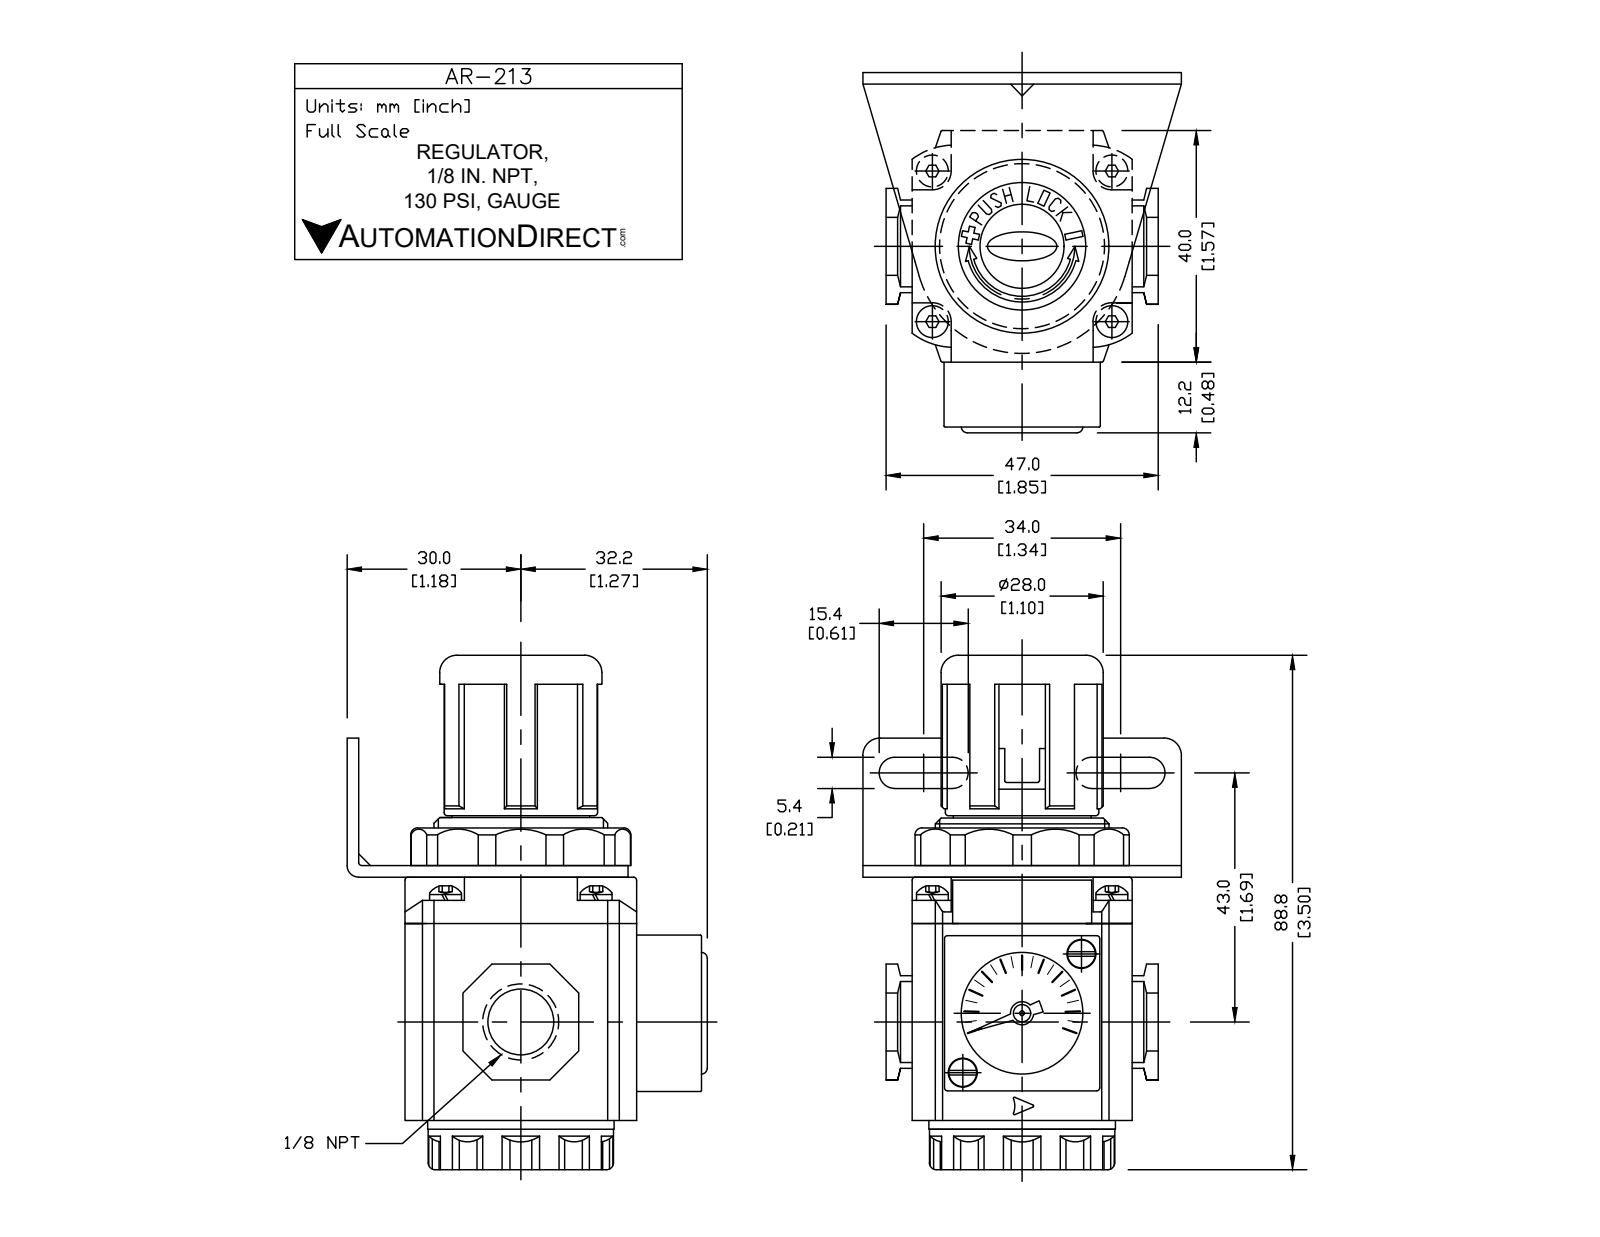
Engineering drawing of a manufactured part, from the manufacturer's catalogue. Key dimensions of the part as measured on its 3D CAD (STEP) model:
Part name (STEP PRODUCT): AR-213
STEP written by: SolidWorks 2015 (CONFIG_CONTROL_DESIGN)
Units: millimetres
Bodies: 14 solids, 491 faces (326 planar, 133 cylindrical, 32 other)
Overall size (bounding box): 88.8 × 62 × 55
Volume: 103 610 mm³ · Surface area: 29 145 mm²
Round holes (diameter × count): ⌀3 ×6, ⌀2 ×1, ⌀8.43 ×1, ⌀21 ×1, ⌀22 ×1, ⌀30 ×1
Round bosses / shafts (diameter × count): ⌀5.5 ×4, ⌀2.7 ×2, ⌀32 ×1, ⌀31.36 ×1, ⌀28 ×1, ⌀23.8 ×1, ⌀14 ×1, ⌀4 ×1
Partial cylindrical surfaces — rounded edges, fillets, slot ends (radius × count): R1.2 ×10, R1 ×8, R3.25 ×6, R0.3 ×4, R2.75 ×4, R12 ×4, R0.2 ×3, R2 ×1
Main face-to-face distances: 2, 42, 10, 44, 39, 40, 38, 50, 1, 11
Hole centre spacings: 20.23, 14.5, 26, 31, 40.46, 28.99
